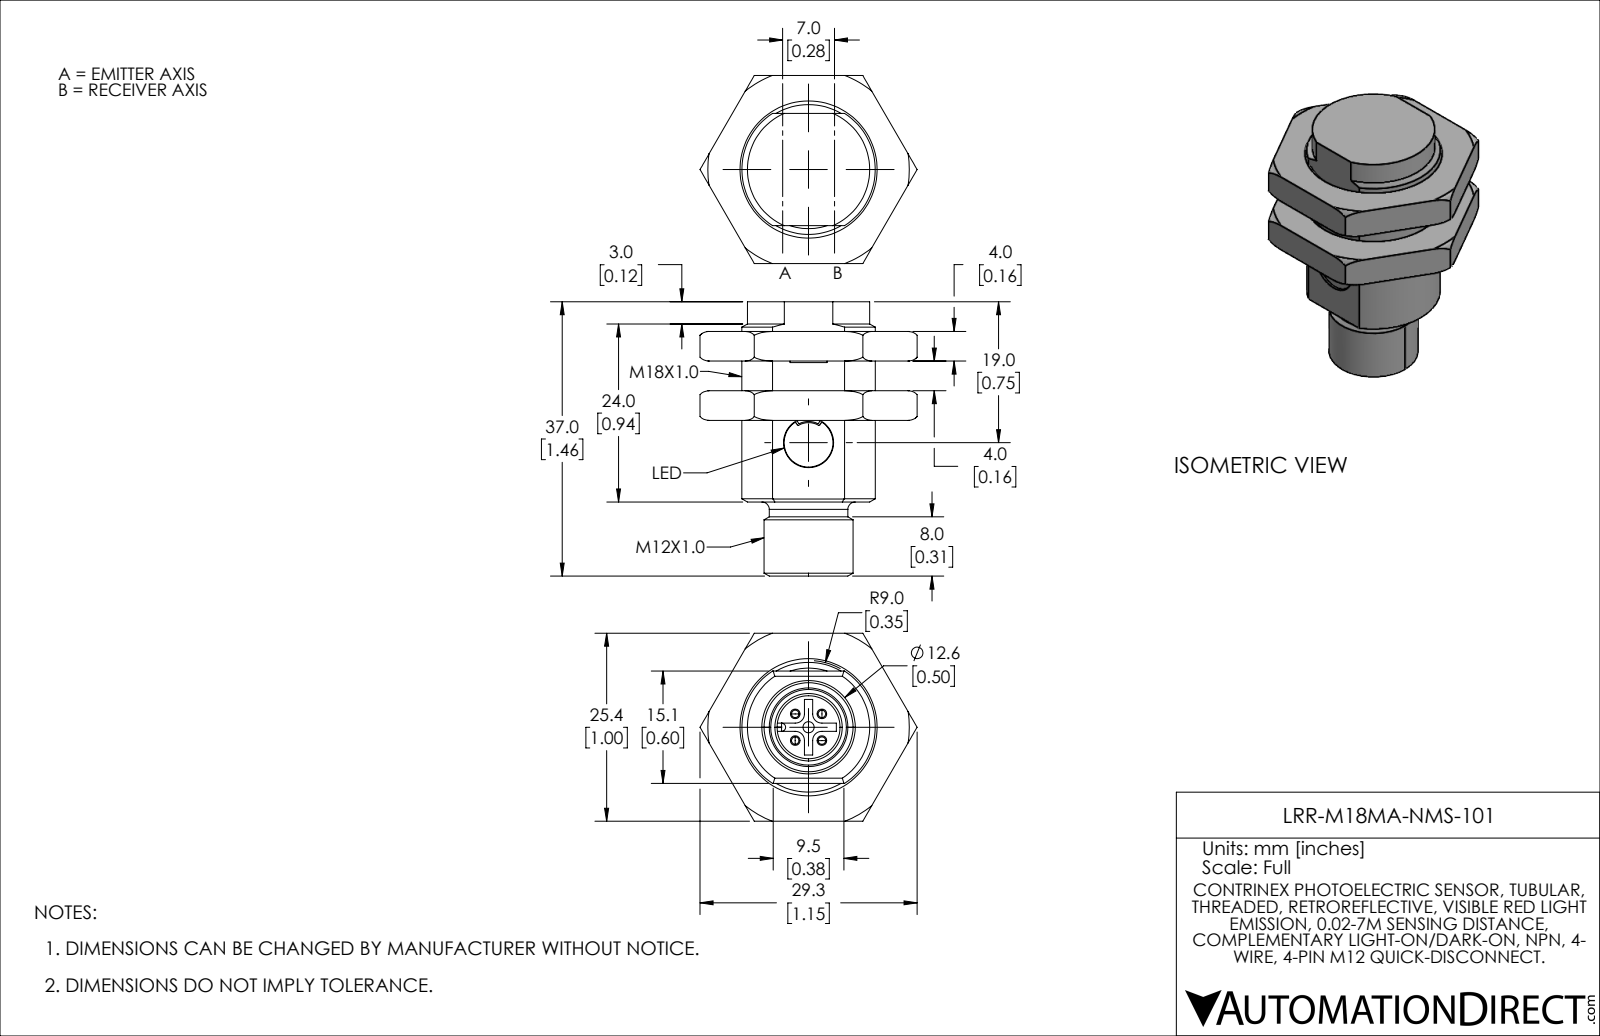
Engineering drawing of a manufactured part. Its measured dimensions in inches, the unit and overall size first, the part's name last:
Units: inches
Overall size (bounding box): 1.457 × 1.153 × 0.998
Round holes (diameter × count): ⌀0.059 ×1, ⌀0.266 ×1, ⌀0.335 ×1, ⌀0.689 ×1
Round bosses / shafts (diameter × count): ⌀0.039 ×4, ⌀0.472 ×1, ⌀0.417 ×1
Partial cylindrical surfaces — rounded edges, fillets, slot ends (radius × count): R0.004 ×4, R0.006 ×4, R0.049 ×4, R0.02 ×2, R0.022 ×1, R0.106 ×1, R0.112 ×1, R0.325 ×1
Main face-to-face distances: 0.157, 0.315, 0.472, 0.998, 0.201, 0.798, 0.597, 0.63, 0.433, 0.591
Volume: 0.572 in³ · Surface area: 7.737 in²
Bodies: 3 solids, 176 faces (65 planar, 50 cylindrical, 61 other)
Part name (STEP PRODUCT): LRR-M18MA-NMS-101
STEP written by: SolidWorks 2021 (AUTOMOTIVE_DESIGN)
